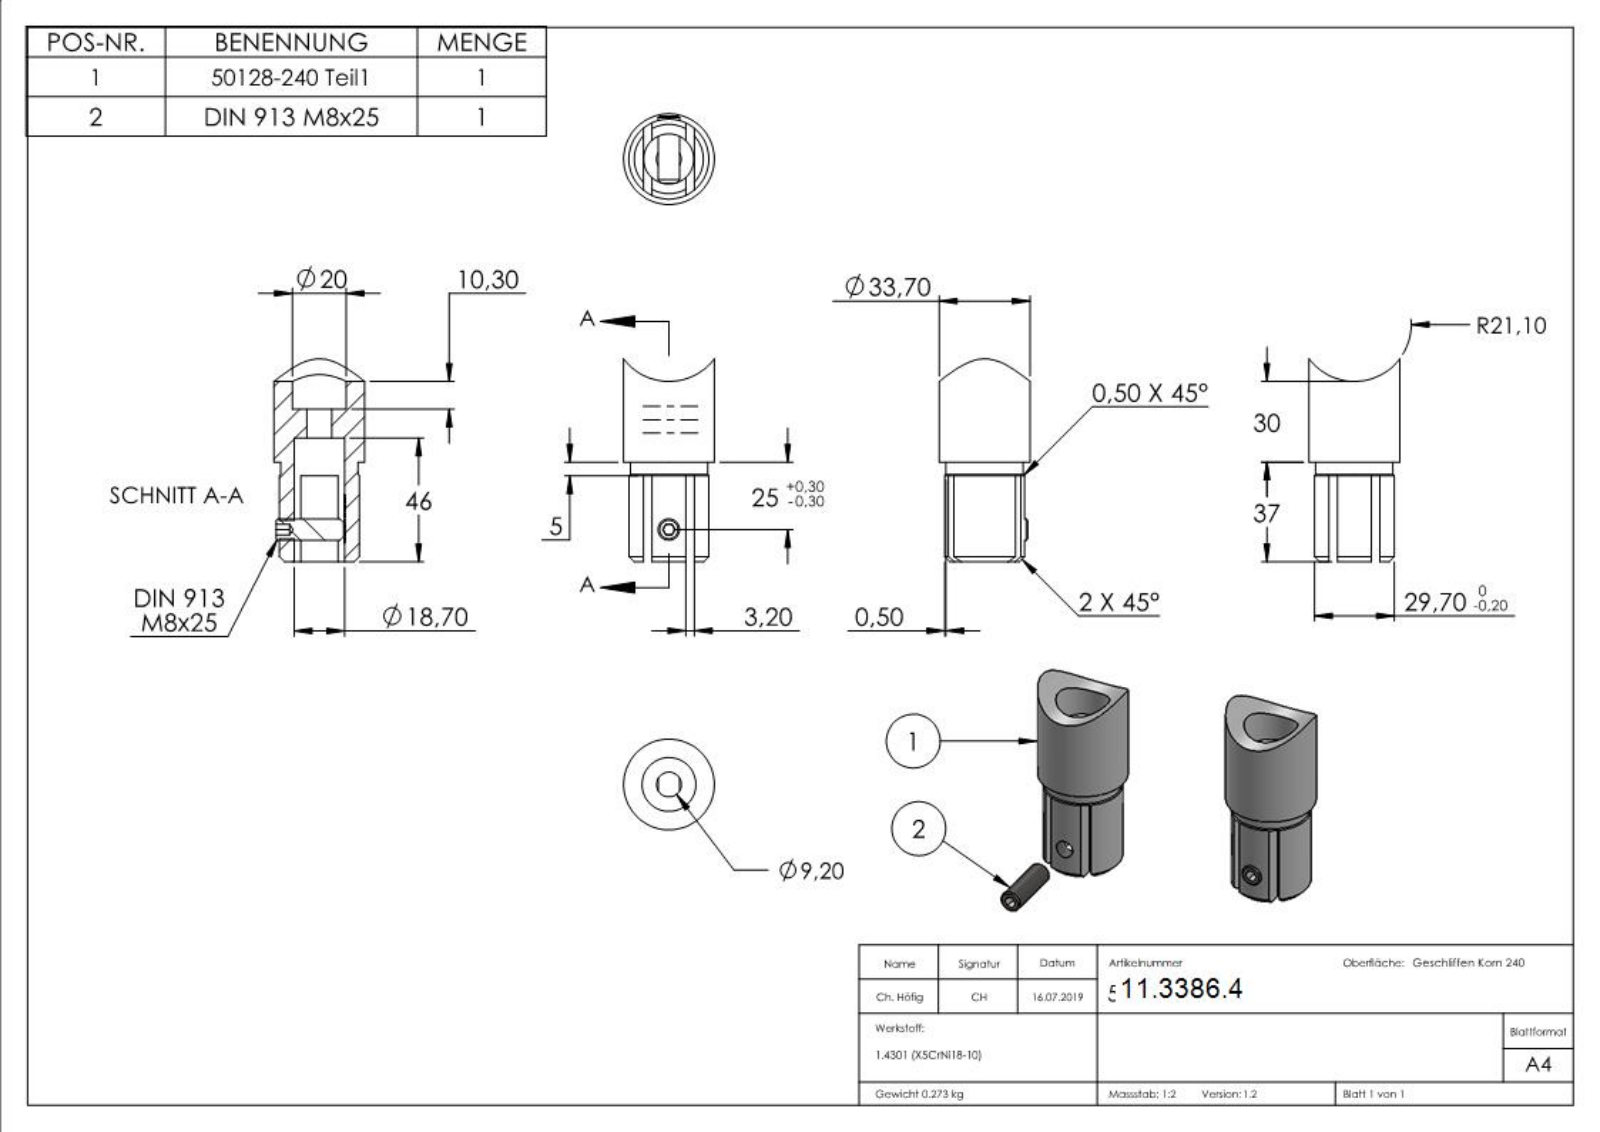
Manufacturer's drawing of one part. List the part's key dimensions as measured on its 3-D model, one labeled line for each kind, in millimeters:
Part name (STEP PRODUCT): 5012X-240 Teil1_50128-240 Teil1; 50128-240; DIN913_DIN 913 M8x25
STEP written by: SolidWorks 2015 (CONFIG_CONTROL_DESIGN)
Units: millimetres
Bodies: 2 solids, 298 faces (124 planar, 58 cylindrical, 116 other)
Overall size (bounding box): 75.4 × 33.7 × 33.7
Volume: 34 600 mm³ · Surface area: 14 095 mm²
Round holes (diameter × count): ⌀6.8 ×1, ⌀9.2 ×1, ⌀18.7 ×1, ⌀20 ×1
Round bosses / shafts (diameter × count): ⌀33.7 ×1, ⌀29.7 ×1, ⌀28.7 ×1, ⌀8 ×1
Partial cylindrical surfaces — rounded edges, fillets, slot ends (radius × count): R9.45 ×1, R21.1 ×1
Main face-to-face distances: 3.2, 15.8, 19, 12.6, 19.7, 9, 10.7, 37, 46, 56.7
